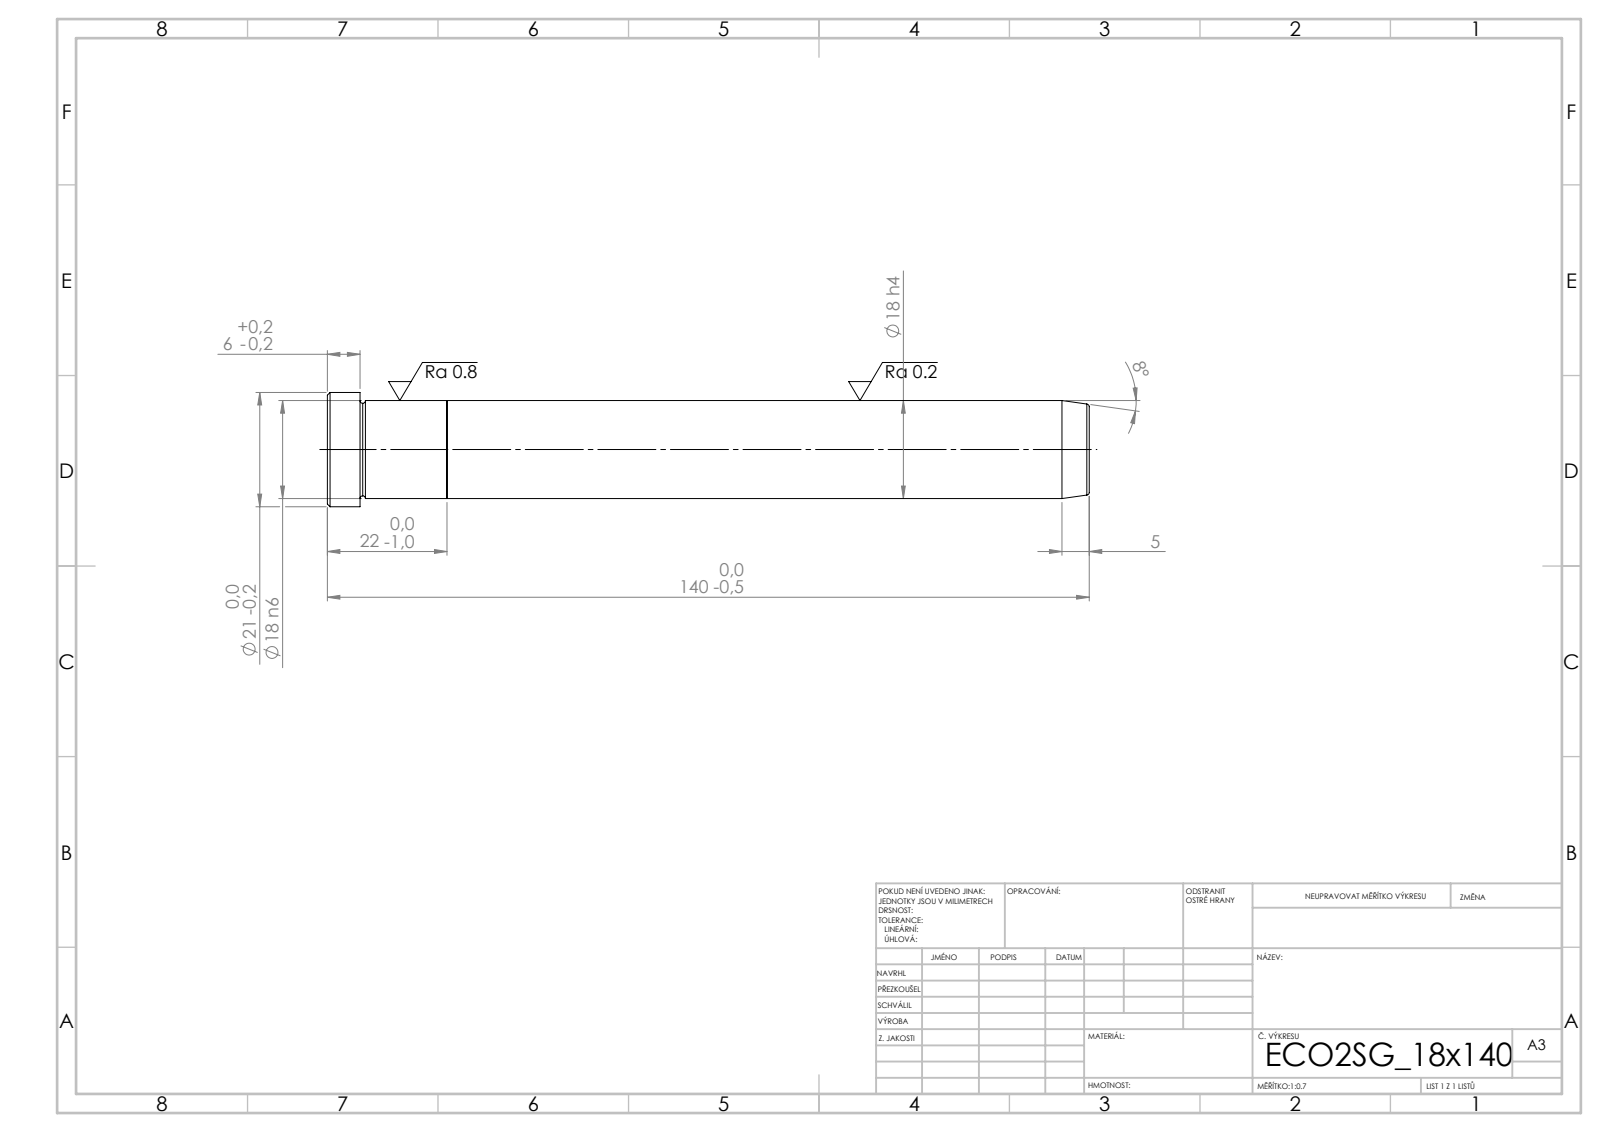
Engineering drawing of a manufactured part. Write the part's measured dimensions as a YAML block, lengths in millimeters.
step_written_by: "SolidWorks 2019 (CONFIG_CONTROL_DESIGN)"
units: millimeters
bodies: {solids: 2, faces: 21, planar: 5, cylindrical: 6, other: 10}
overall_size: [140, 21, 21]
volume: 36048
surface_area: 9130
round_bosses_or_shafts:
  - {diameter: 21, count: 1}
  - {diameter: 18, count: 1}
face_to_face_distances: [22, 118, 140, 134, 16, 6]
